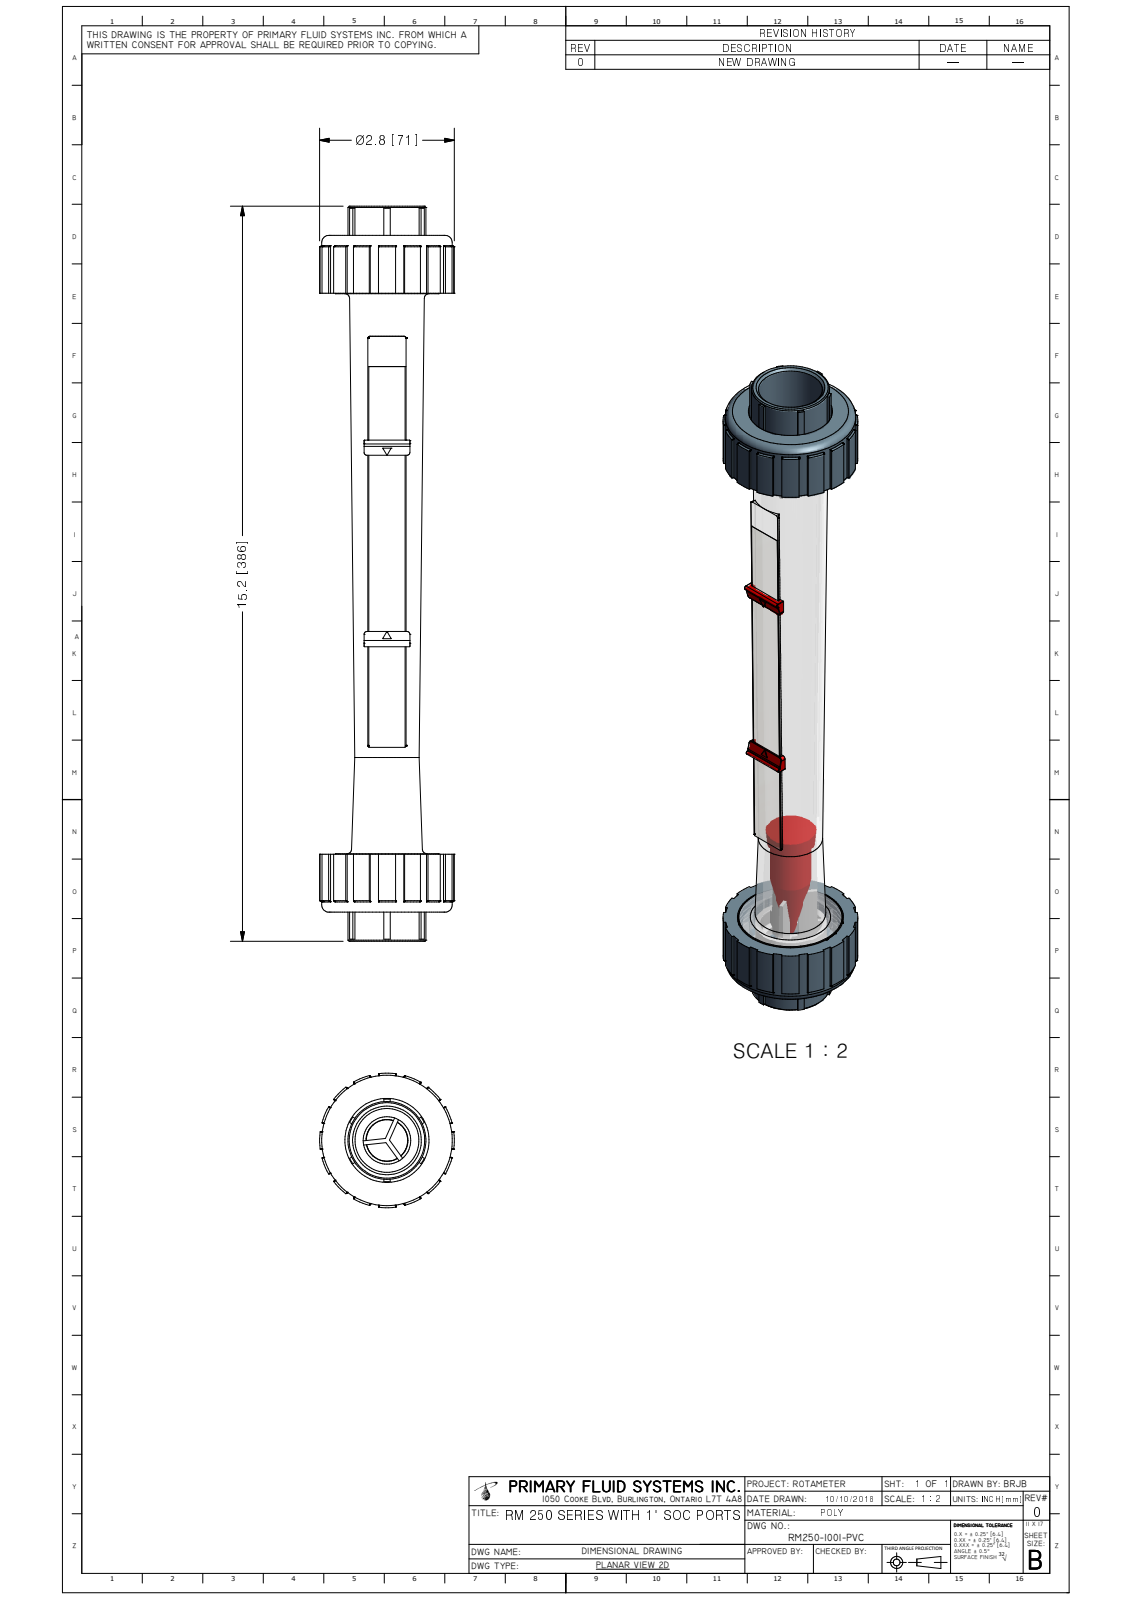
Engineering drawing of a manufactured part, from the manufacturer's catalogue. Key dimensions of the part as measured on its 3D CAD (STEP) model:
Part name (STEP PRODUCT): RM250-100I-PVC_R0
STEP written by: Autodesk Inventor 2009 (AUTOMOTIVE_DESIGN)
Units: inches
Bodies: 1 solid, 571 faces (234 planar, 138 cylindrical, 199 other)
Overall size (bounding box): 15.2 × 2.783 × 2.783
Volume: 31.79 in³ · Surface area: 173 in²
Round holes (diameter × count): ⌀1.32 ×1, ⌀1.738 ×1, ⌀2.19 ×1
Round bosses / shafts (diameter × count): ⌀2.697 ×1, ⌀2.152 ×1, ⌀2.022 ×1, ⌀1.61 ×1, ⌀1.485 ×1
Partial cylindrical surfaces — rounded edges, fillets, slot ends (radius × count): R0.008 ×18, R0.01 ×16, R0.004 ×10, R0.006 ×4, R0.06 ×4, R0.008 ×2, R0.04 ×2, R0.045 ×2
Main face-to-face distances: 1.197, 12.799, 0.367, 13.629, 0.83, 12.432, 1.207, 12.789, 11.592, 0.84
